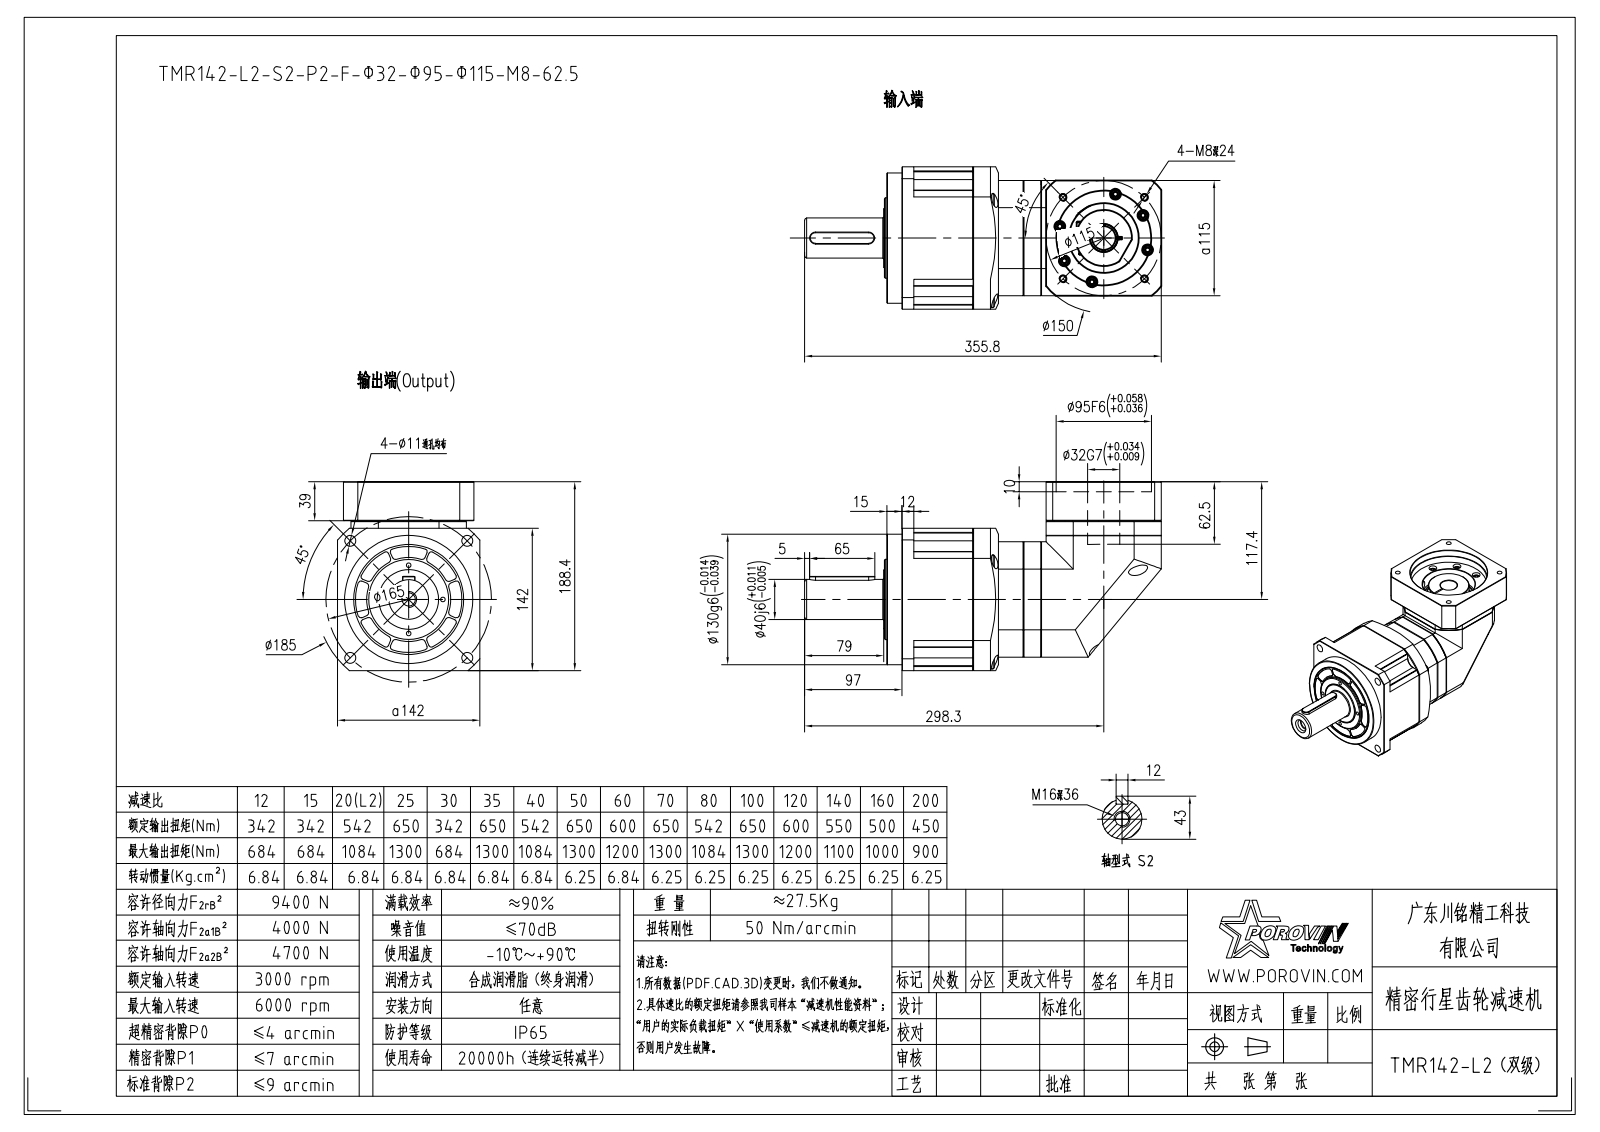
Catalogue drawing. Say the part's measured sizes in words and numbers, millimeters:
The part is named "HEXAGON_SOCKET_HEAD_CAP_S-25569; SPRING_LOCK_WASHERS--NORMAL_TYP; HEXAGON_SOCKET_HEAD_CAP_S-25446; HEXAGON_SOCKET_HEAD_CAP_S-25512 (+8 more)". Its 3-D file was written by "CREO PARAMETRIC BY PTC INC, 2020053 (CONFIG_CONTROL_DESIGN)". It is 49 solids with 1522 faces: 639 planar, 591 cylindrical and 292 other. Overall it measures 355.8 by 188.4 by 142 millimeters. Its volume is 4 038 000 cubic millimeters and its surface area 422 576 square millimeters. Round holes: 17 of diameter 6.68, 13 of diameter 5, 12 of diameter 11, 11 of diameter 6.8, 10 of diameter 6.5, 6 of diameter 6.6, 5 of diameter 14, 4 of diameter 9, 4 of diameter 10.5, 4 of diameter 11.9, 1 of diameter 8.5, 1 of diameter 13.6. Round bosses or shafts: 17 of diameter 10, 17 of diameter 9.88, 17 of diameter 6, 5 of diameter 13, 5 of diameter 8, 1 of diameter 130, 1 of diameter 99, 1 of diameter 80. Partial cylindrical surfaces (rounded edges, fillets, slot ends): 40 of radius 1, 32 of radius 2, 4 of radius 10.5, 2 of radius 6, 2 of radius 65, 1 of radius 5, 1 of radius 6.75, 1 of radius 42.5. The main face-to-face distances are 13.5, 128.5, 50.3, 18, 115, 68.3, 68.1, 17.8, 142, 14.9. The hole center spacings are 41.23, 45.25, 97.08, 12.31, 21.17, 47.5, 91.96, 110.07.
